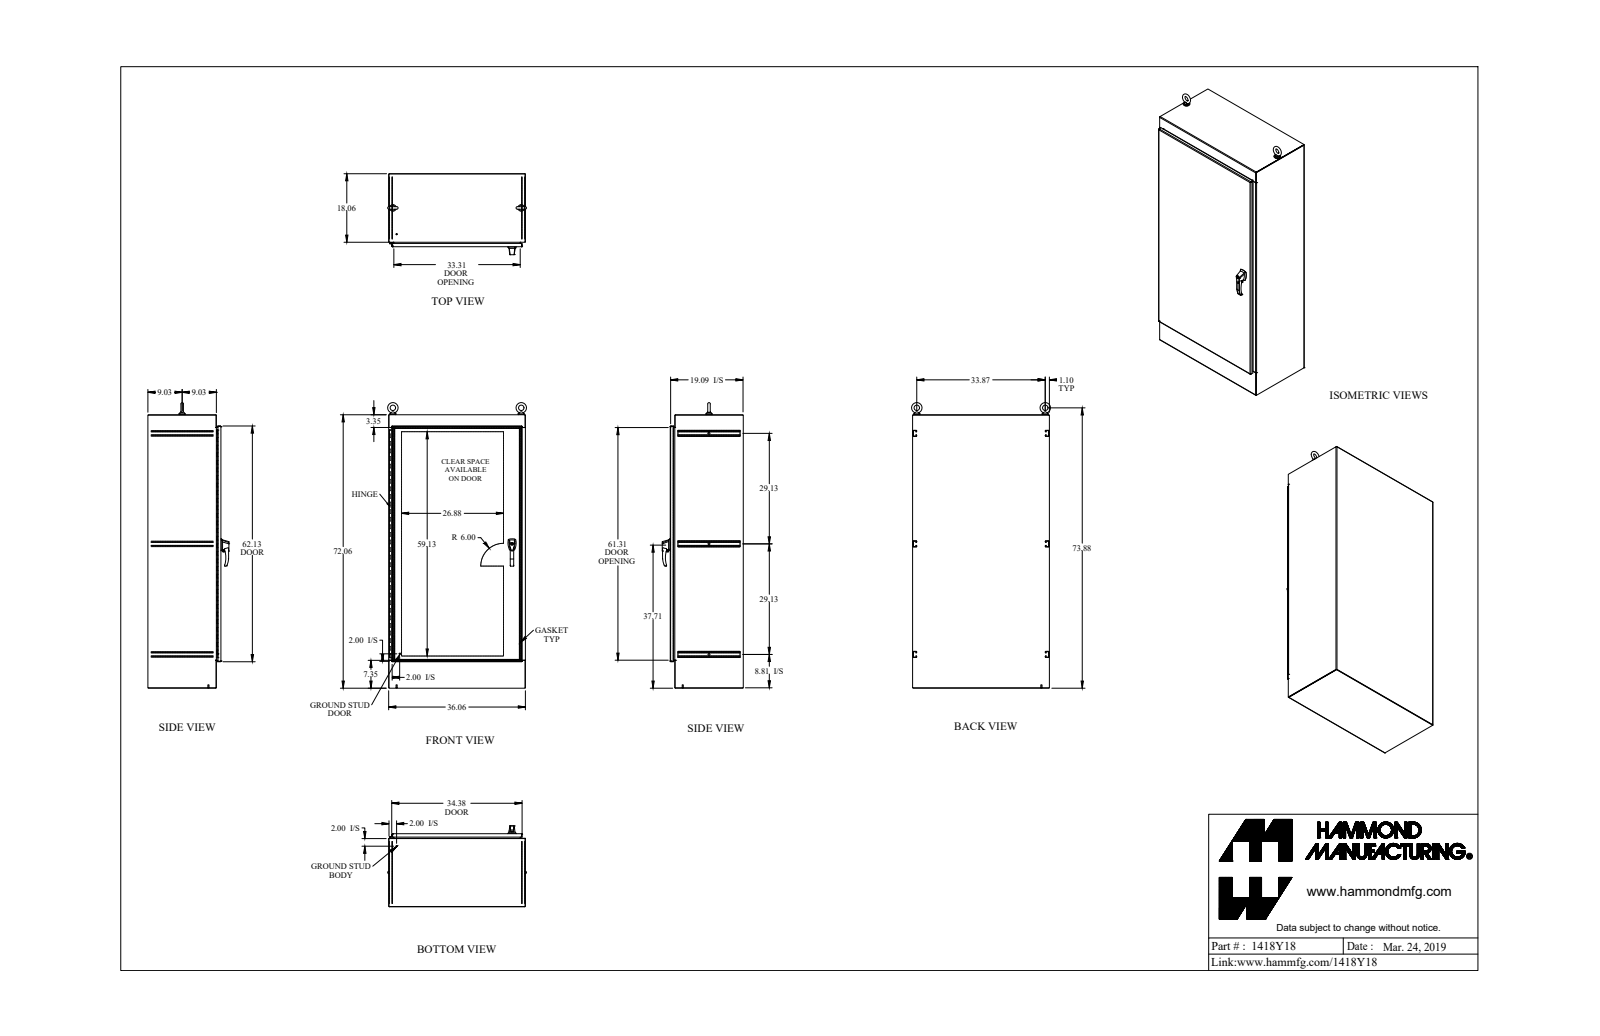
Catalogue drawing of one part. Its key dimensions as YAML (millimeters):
part_name: "1418Y18_Default"
step_written_by: "SolidWorks 2019 (CONFIG_CONTROL_DESIGN)"
units: millimeters
bodies: {solids: 52, faces: 1742, planar: 781, cylindrical: 796, other: 165}
overall_size: [1923.1, 942.8, 542.6]
volume: 16620000
surface_area: 13810000
round_holes:
  - {diameter: 7.7, count: 10}
  - {diameter: 19.1, count: 4}
  - {diameter: 12.7, count: 3}
  - {diameter: 6.4, count: 2}
  - {diameter: 6.5, count: 2}
  - {diameter: 7.1, count: 2}
  - {diameter: 7.1, count: 2}
  - {diameter: 8, count: 2}
  - {diameter: 9.9, count: 2}
  - {diameter: 10.5, count: 2}
  - {diameter: 13.4, count: 2}
  - {diameter: 15.9, count: 2}
round_bosses_or_shafts:
  - {diameter: 7.1, count: 4}
  - {diameter: 44.5, count: 2}
  - {diameter: 38.1, count: 2}
  - {diameter: 31.8, count: 2}
  - {diameter: 25.4, count: 2}
  - {diameter: 19.1, count: 2}
  - {diameter: 18.7, count: 2}
  - {diameter: 16, count: 2}
partial_cylinders:
  - {radius: 1.1, count: 42}
  - {radius: 3.5, count: 36}
  - {radius: 3.2, count: 22}
  - {radius: 0.5, count: 16}
  - {radius: 1.2, count: 14}
  - {radius: 3.6, count: 14}
  - {radius: 1.5, count: 10}
  - {radius: 8.1, count: 7}
face_to_face_distances: [2.4, 2.4, 913.5, 484, 486.5, 486.5, 488.9, 911.1, 1827.9, 915.9]
hole_center_spacings: [152.4, 304.8, 457.2, 609.6, 762, 860.3, 914.4, 1066.8]
